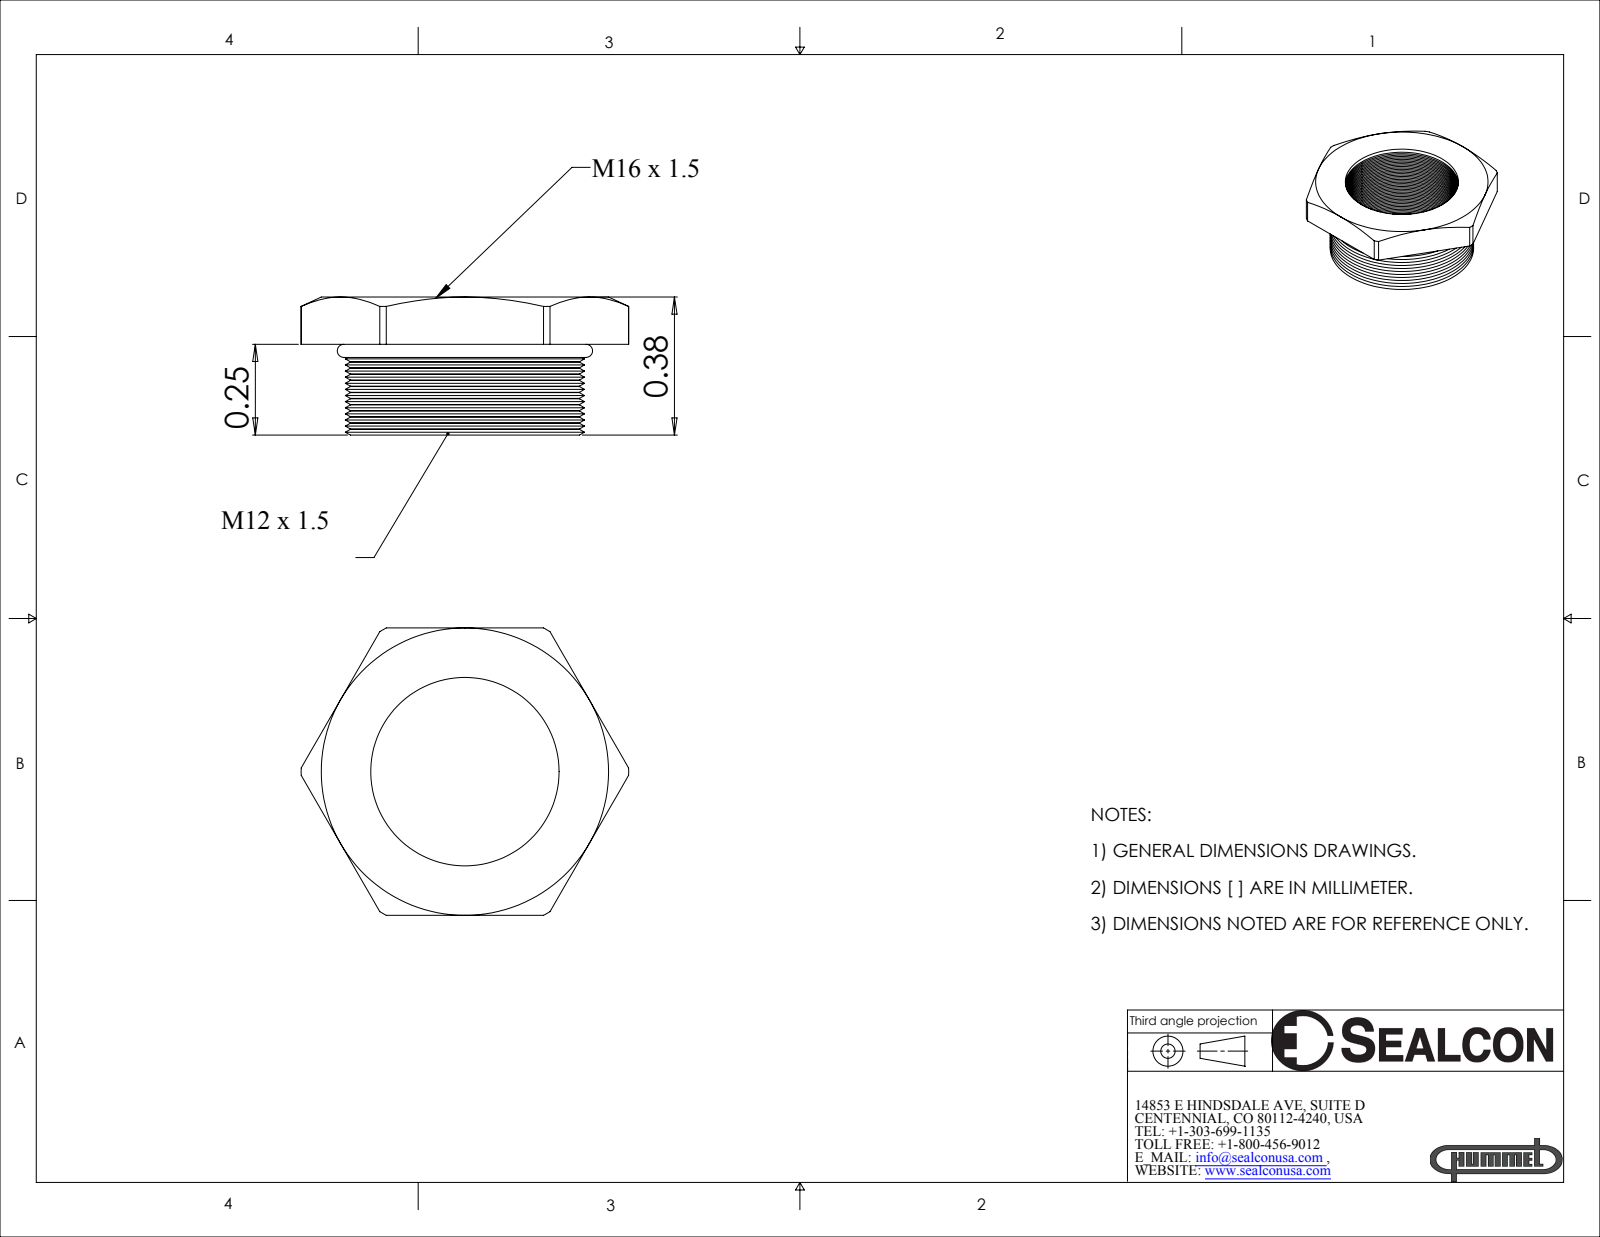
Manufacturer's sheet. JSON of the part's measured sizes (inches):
{"part_name": "RM-1612-SS-B", "step_written_by": "SolidWorks 2008 (CONFIG_CONTROL_DESIGN)", "units": "inches", "bodies": {"solids": 2, "faces": 245, "planar": 9, "cylindrical": 81, "other": 155}, "overall_size": [0.901, 0.79, 0.38], "volume_in3": 0.07, "surface_area_in2": 3.373, "round_holes": [[0.518, 1]], "round_bosses_or_shafts": [[0.63, 1]], "partial_cylinders_radius": [[0.45, 1]], "face_to_face_distances": [0.13, 0.79, 0.24, 0.37]}
